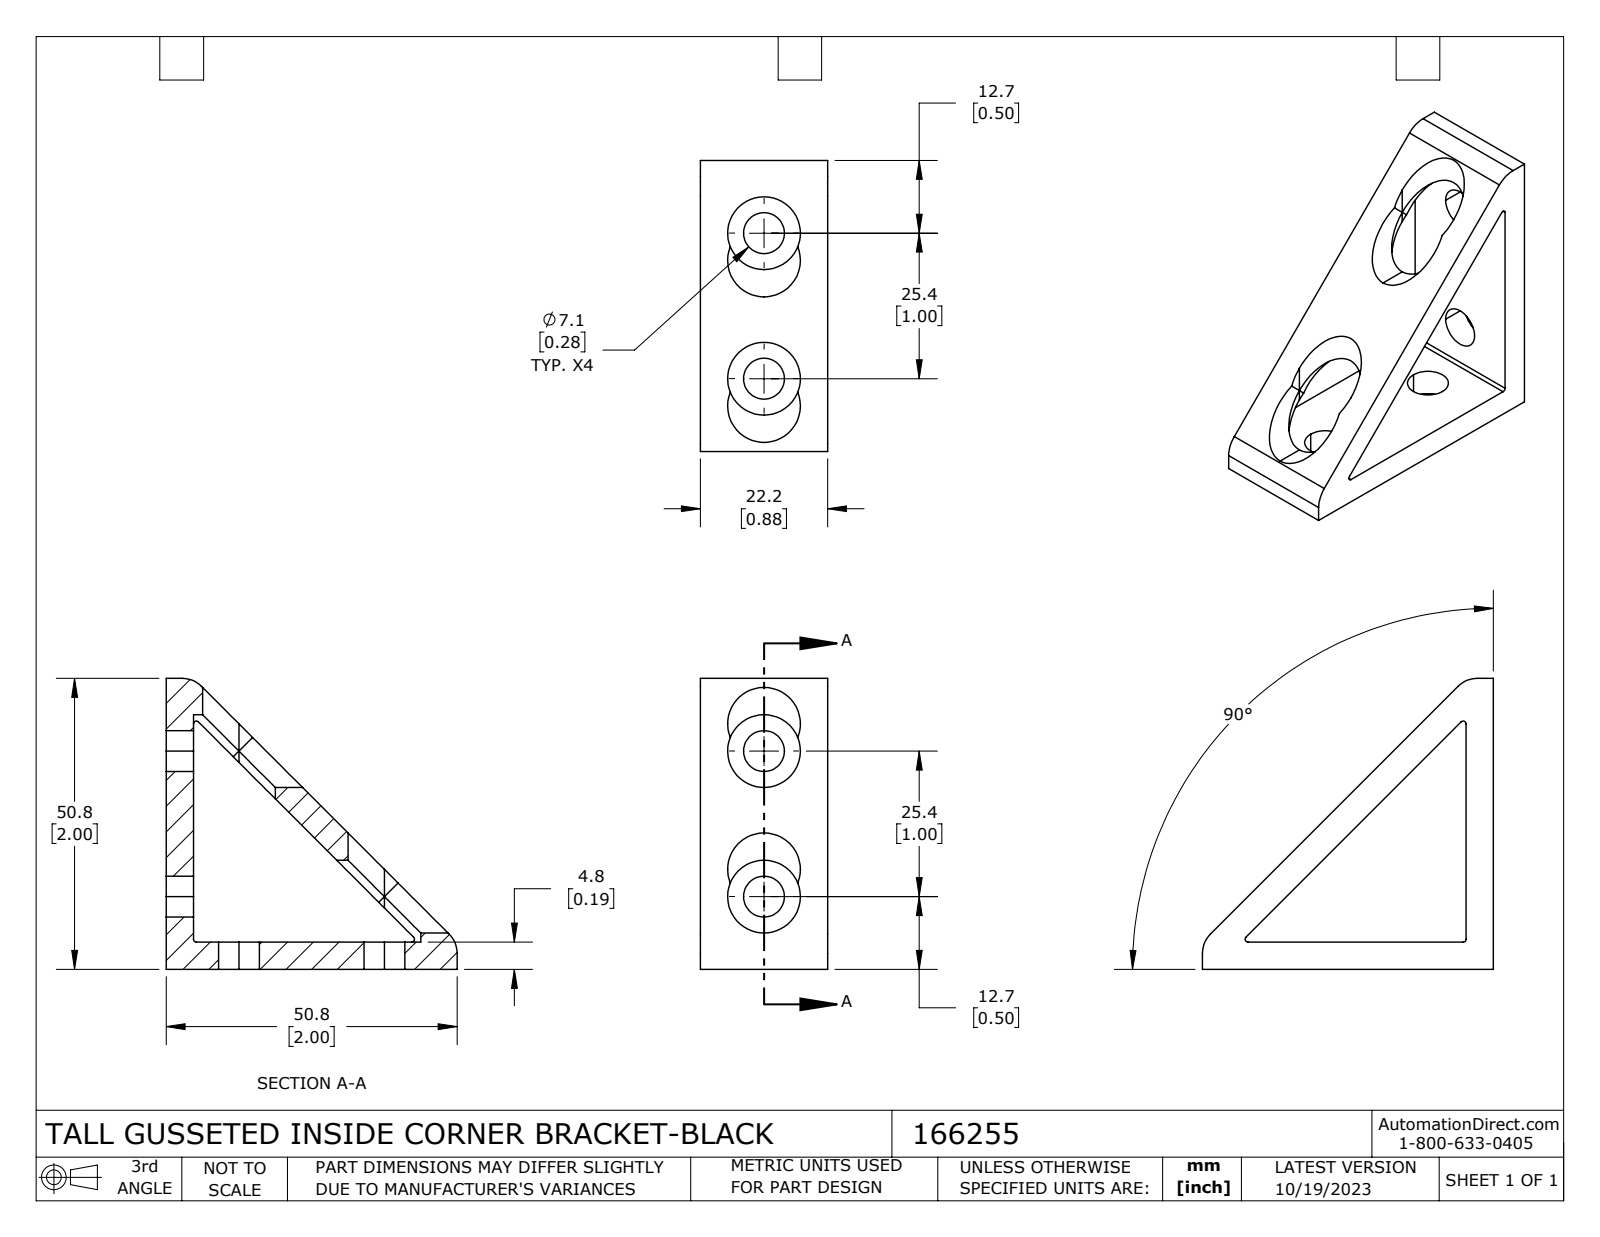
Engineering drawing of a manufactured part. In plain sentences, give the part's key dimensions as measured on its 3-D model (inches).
The part is named "166255". Its 3-D file was written by "SolidWorks 2023 (CONFIG_CONTROL_DESIGN)". It is 1 solid with 43 faces: 10 planar, 33 cylindrical and 0 other. Overall it measures 2 by 2 by 0.875 inches. Its volume is 0.844 cubic inches and its surface area 12.54 square inches. Round holes: 4 of diameter 0.281, 4 of diameter 0.5. Partial cylindrical surfaces (rounded edges, fillets, slot ends): 3 of radius 0.02, 2 of radius 0.187. The main face-to-face distances are 0.187, 0.875, 2, 1.813. The hole center spacings are 1.
